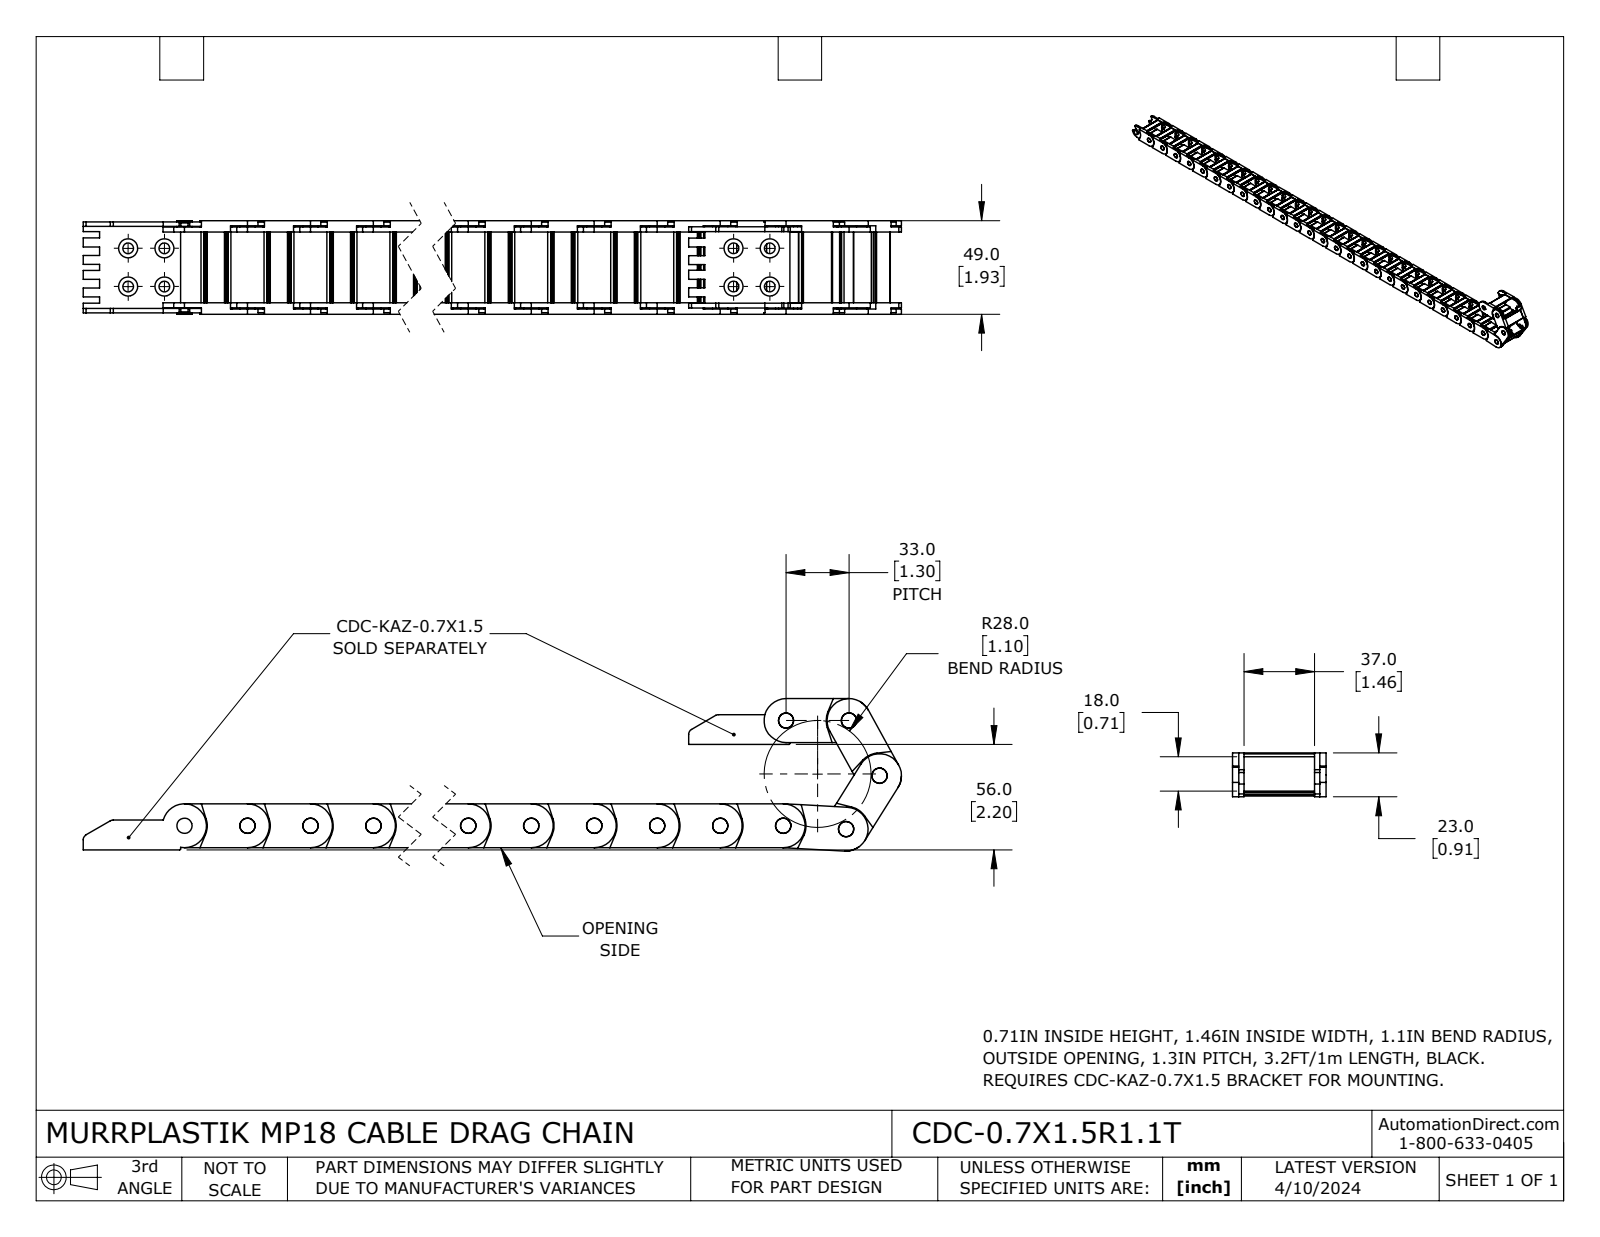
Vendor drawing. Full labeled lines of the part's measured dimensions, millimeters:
Part name (STEP PRODUCT): CDC-0.7X1.5R1.1T
STEP written by: SolidWorks 2023 (CONFIG_CONTROL_DESIGN)
Units: millimetres
Bodies: 30 solids, 2280 faces (1110 planar, 1170 cylindrical, 0 other)
Overall size (bounding box): 931.1 × 79.8 × 49
Volume: 289 400 mm³ · Surface area: 238 800 mm²
Round holes (diameter × count): ⌀8 ×30
Round bosses / shafts (diameter × count): ⌀8 ×1
Partial cylindrical surfaces — rounded edges, fillets, slot ends (radius × count): R0.5 ×120, R1.5 ×120, R0.2 ×60, R0.3 ×60, R11.5 ×31, R11.9 ×31, R5 ×30, R5.5 ×30
Main face-to-face distances: 43, 2.7, 3.3, 6, 49, 45.7, 39.7, 46.3, 0.6, 40.3
Hole centre spacings: 33, 66, 99, 132, 165, 198, 231, 264
